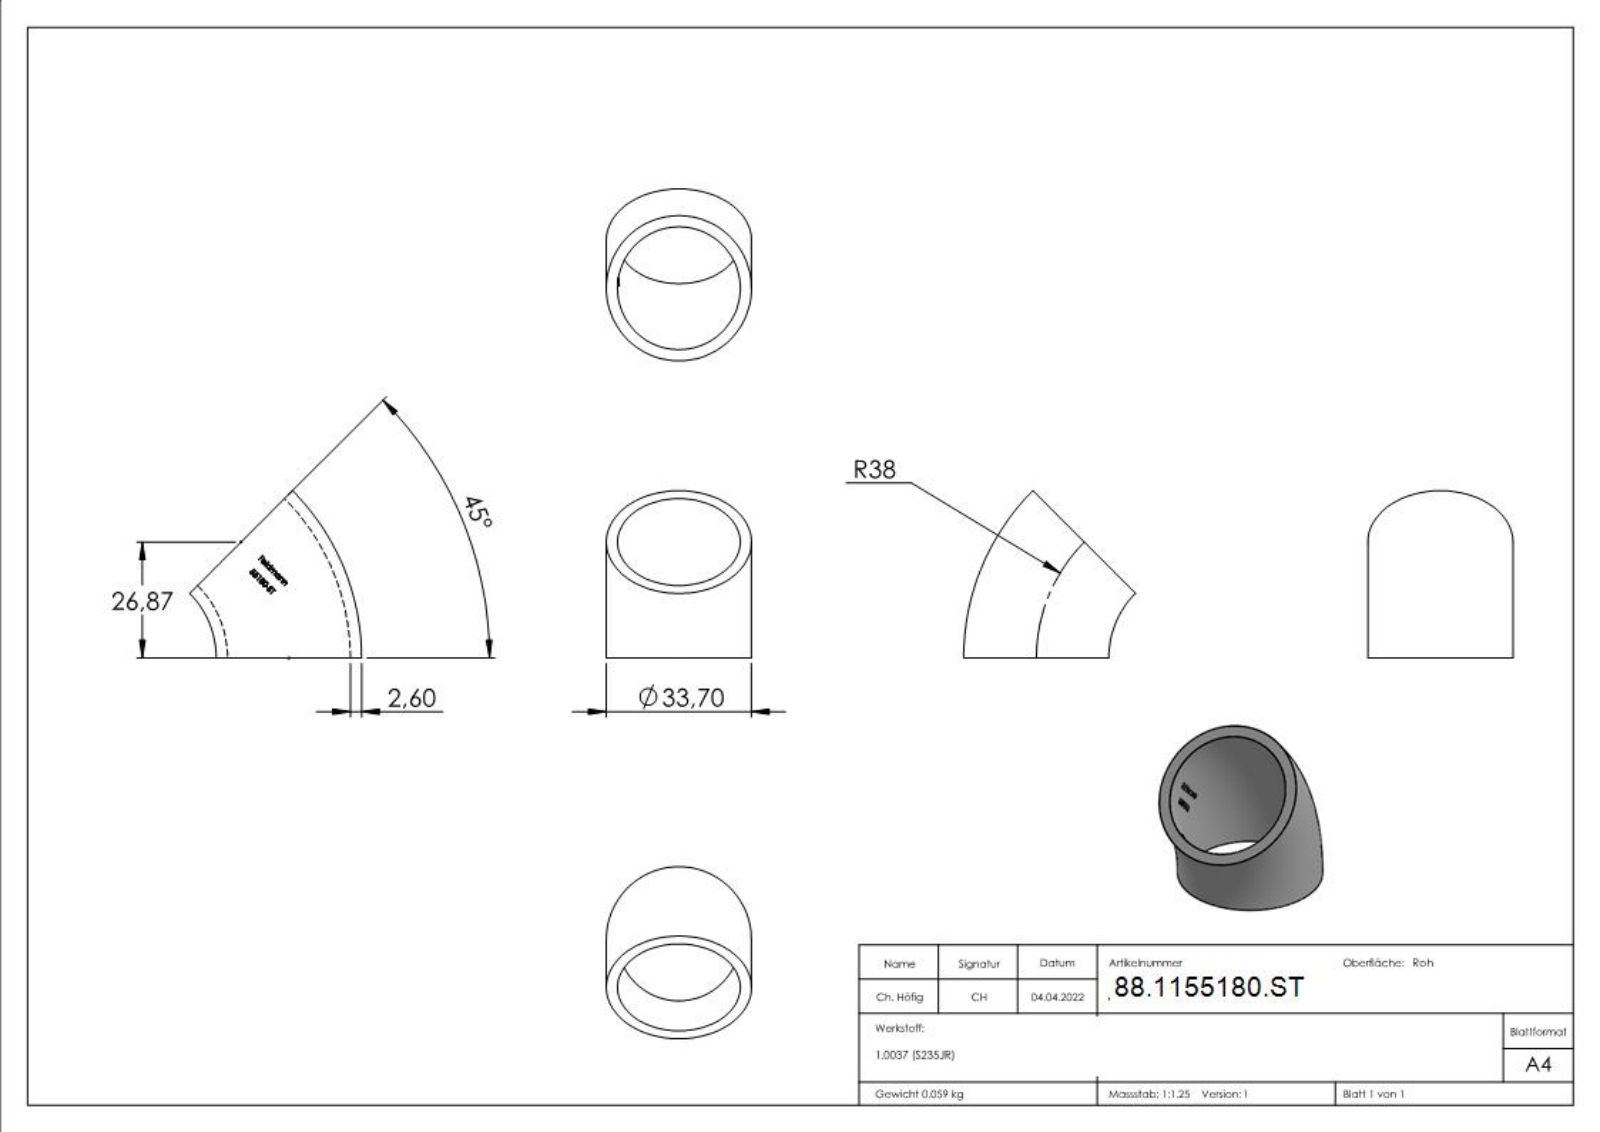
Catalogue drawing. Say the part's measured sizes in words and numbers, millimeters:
The part is named "55180-ST". Its 3-D file was written by "SolidWorks 2018 (CONFIG_CONTROL_DESIGN)". It is 1 solid with 217 faces: 88 planar, 0 cylindrical and 129 other. Overall it measures 39.9 by 38.78 by 33.7 millimeters. Its volume is 7 581 cubic millimeters and its surface area 6 349 square millimeters. The main face-to-face distances are 3.09, 3.26, 4.44, 1.23, 3.38, 2.97, 7.53, 2.96, 1.9, 3.67.
